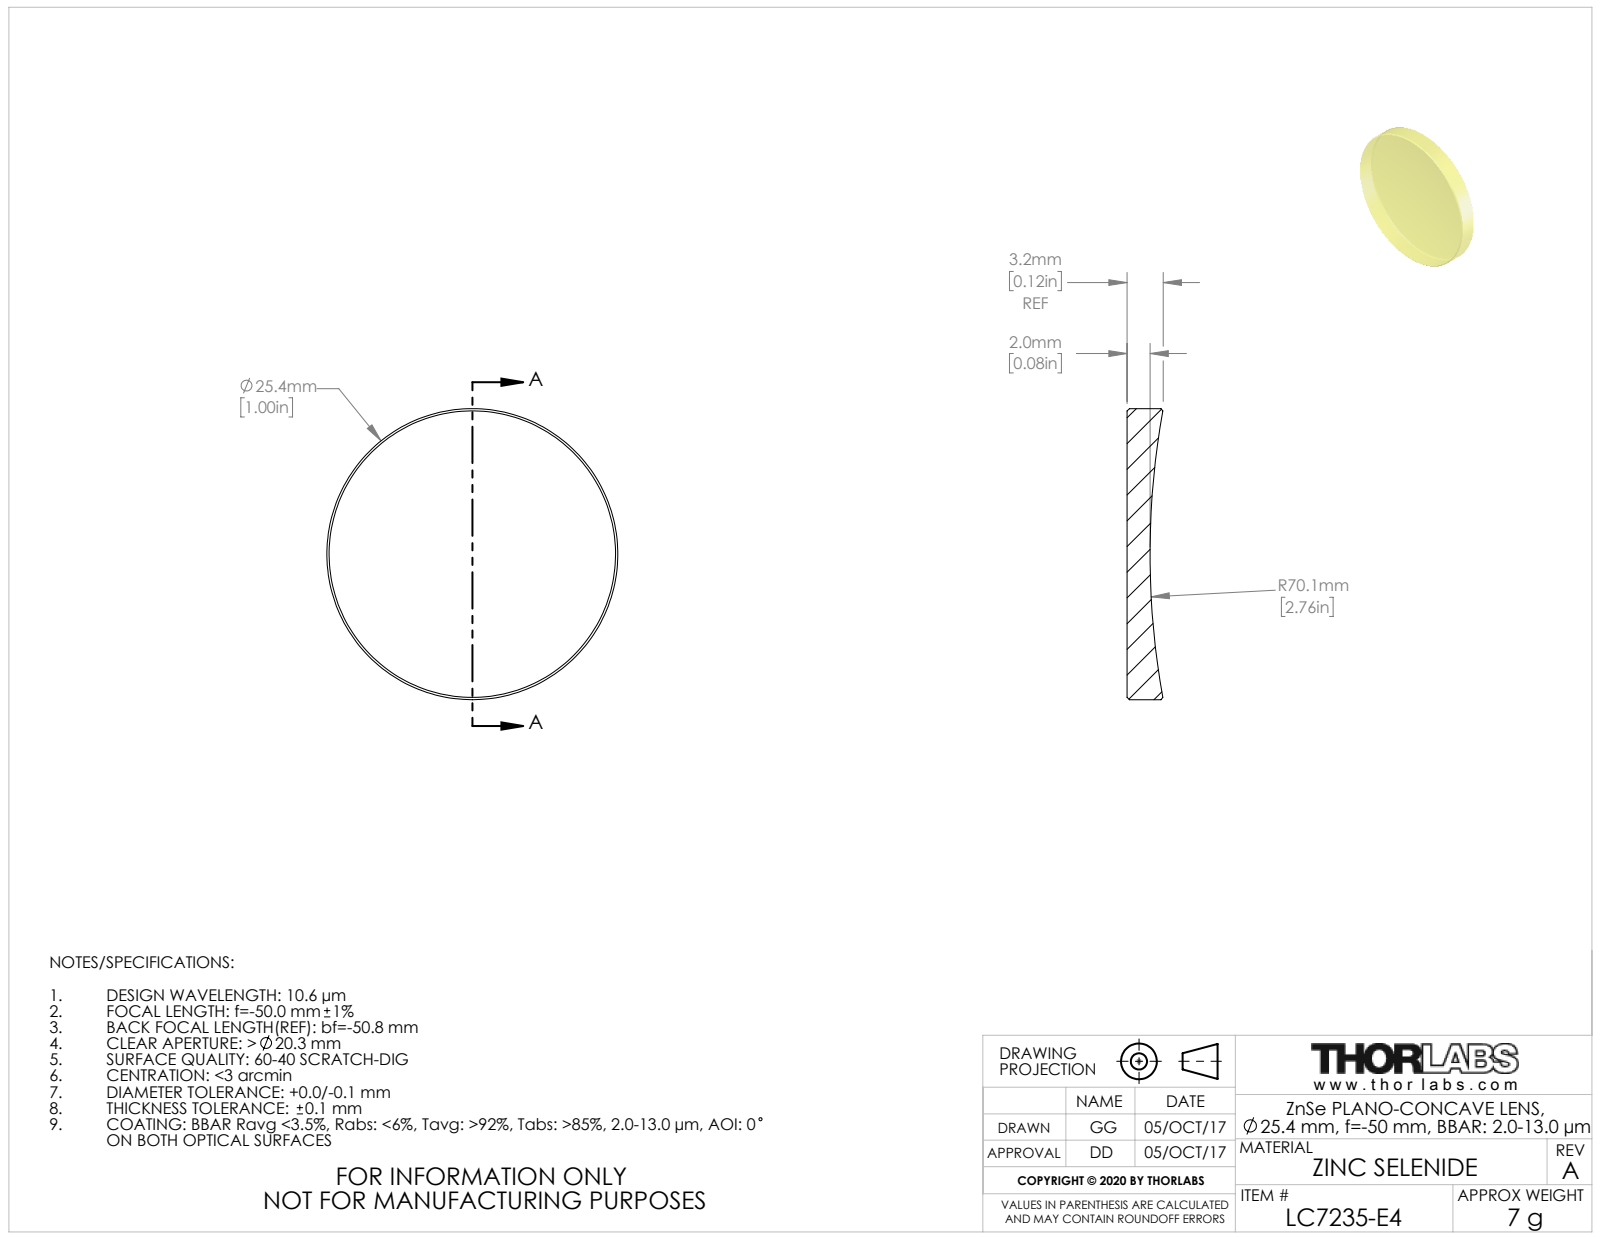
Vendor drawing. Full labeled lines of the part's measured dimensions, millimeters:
Part name (STEP PRODUCT): TTN099138-E0W
STEP written by: SolidWorks 2018 (CONFIG_CONTROL_DESIGN)
Units: millimetres
Bodies: 1 solid, 9 faces (1 planar, 2 cylindrical, 6 other)
Overall size (bounding box): 25.4 × 25.4 × 3.12
Volume: 1 303 mm³ · Surface area: 1 249 mm²
Round bosses / shafts (diameter × count): ⌀25.4 ×1
